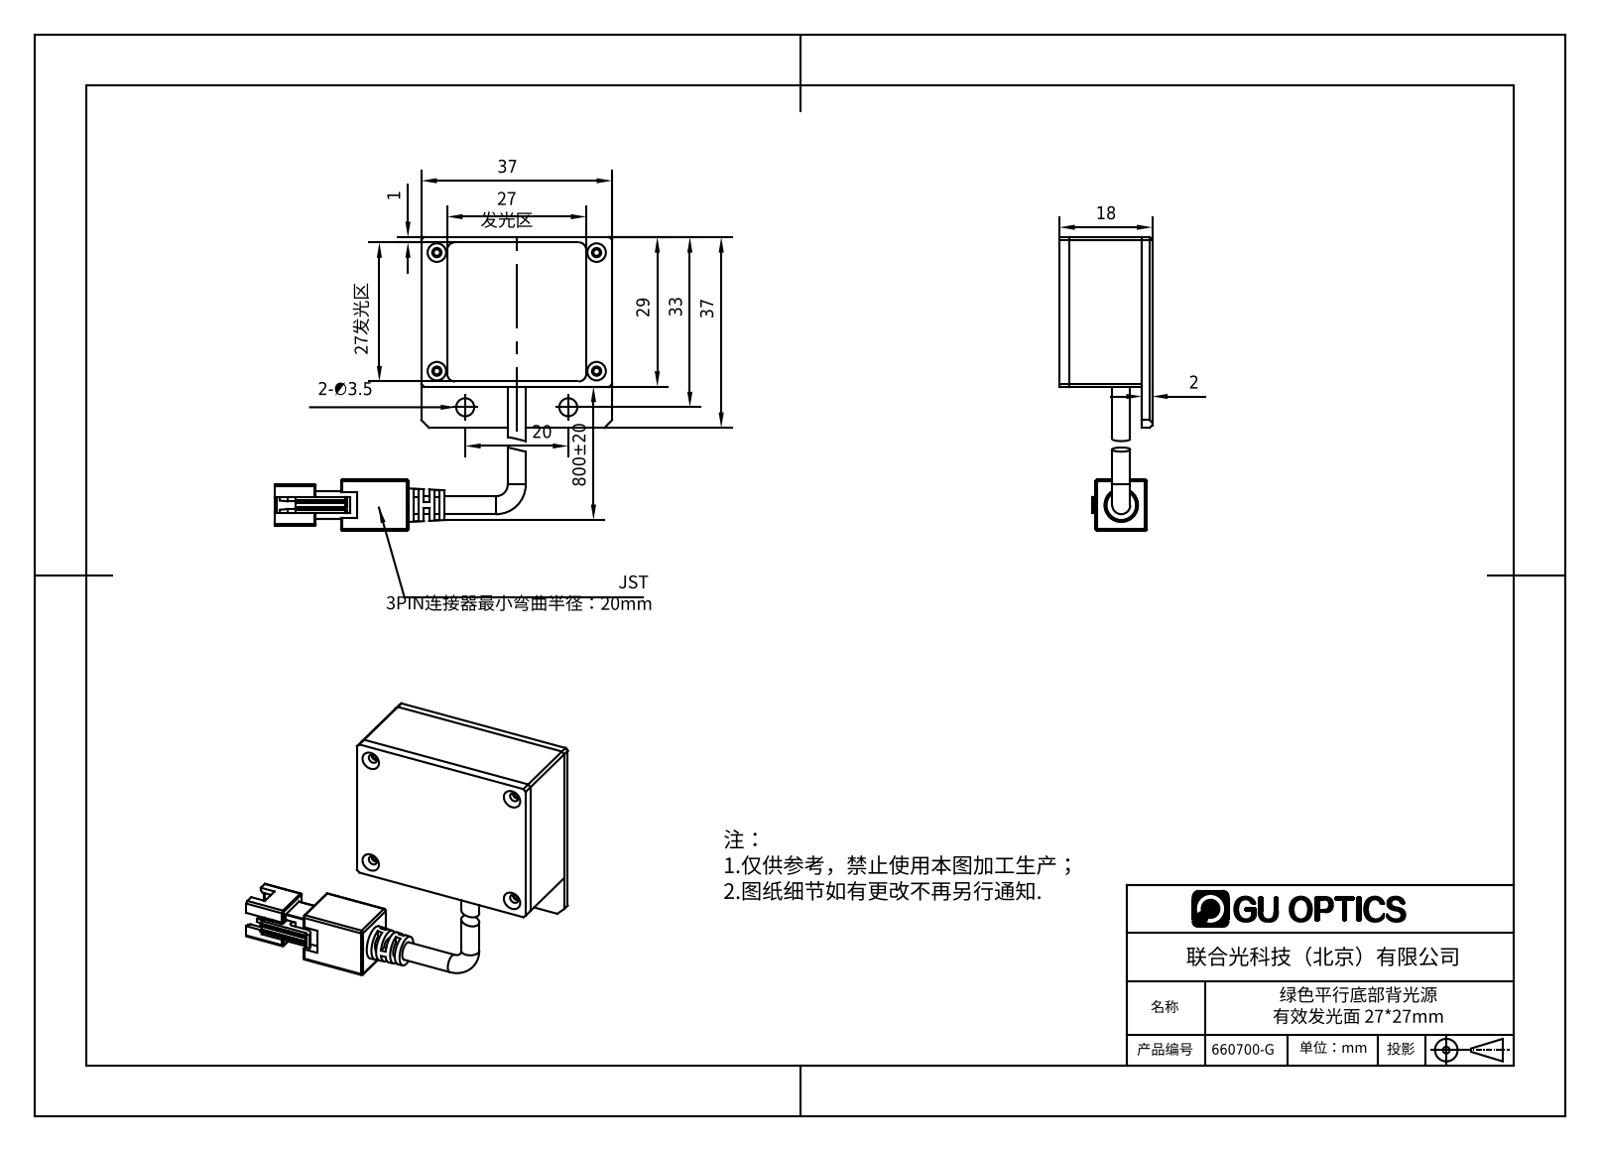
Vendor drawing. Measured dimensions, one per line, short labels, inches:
name: 660700-G
written by: SolidWorks 2016 (AUTOMOTIVE_DESIGN)
unit: in
bodies: 6 solids, 470 faces (229 planar, 122 cylindrical, 119 other)
size: 2.579 × 2.244 × 0.713
volume: 0.709 in³; area: 20.31 in²
holes: 4× ⌀0.049, 4× ⌀0.063, 4× ⌀0.071, 4× ⌀0.079, 4× ⌀0.094, 2× ⌀0.138
bosses: 2× ⌀0.138
rounds: 15× R0.004, 13× R0.008, 12× R0.016, 4× R0.039, 4× R0.059, 1× R0.012, 1× R0.027, 1× R0.055
face distances: 0.63, 0.079, 0.551, 0.709, 0.039, 1.102, 0.197, 0.083, 0.713, 0.634
hole spacings: 0.35, 0.906, 1.041, 1.201, 1.22, 1.52, 1.55, 0.787
